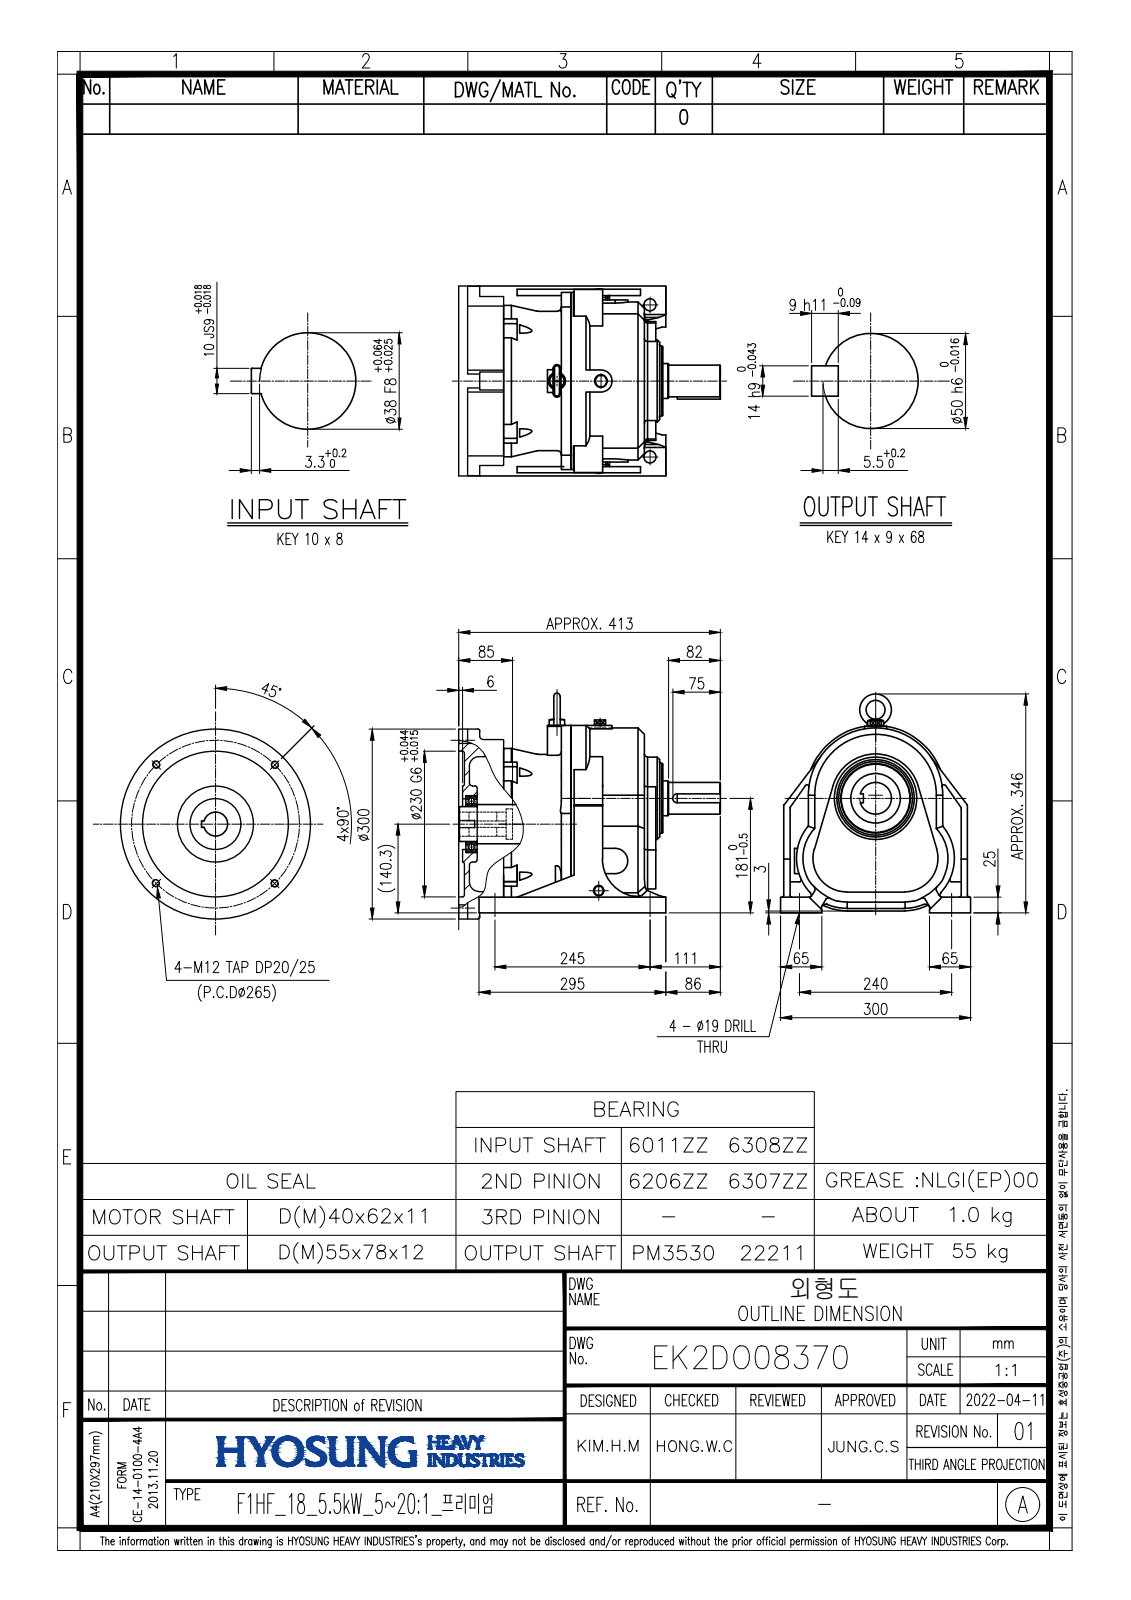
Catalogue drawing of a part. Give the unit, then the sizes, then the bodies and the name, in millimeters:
Units: millimetres
Overall size (bounding box): 413 × 356.75 × 309
Round holes (diameter × count): ⌀10.2 ×5, ⌀10 ×4, ⌀19 ×4, ⌀2.7 ×2, ⌀6.8 ×2, ⌀13 ×2, ⌀14 ×2, ⌀4 ×1, ⌀8.5 ×1, ⌀38 ×1, ⌀48 ×1, ⌀59.6 ×1
Round bosses / shafts (diameter × count): ⌀55 ×2, ⌀300 ×1, ⌀220 ×1, ⌀130 ×1, ⌀110 ×1, ⌀66.41 ×1, ⌀50 ×1, ⌀12 ×1
Partial cylindrical surfaces — rounded edges, fillets, slot ends (radius × count): R5 ×59, R7 ×17, R6 ×10, R11 ×6, R1 ×4, R12.5 ×4, R83 ×4, R3 ×3
Main face-to-face distances: 5, 9, 18, 153, 311, 295, 162, 302, 149, 25
Hole centre spacings: 181.81, 132.5, 8, 98.62, 101.41, 124.49, 176.06, 187.38
Volume: 16 850 000 mm³ · Surface area: 625 124 mm²
Bodies: 4 solids, 586 faces (263 planar, 197 cylindrical, 126 other)
Part name (STEP PRODUCT): EK2DO08370H001_F1HM18_5.5KW_R5~20_defeature
STEP written by: SolidWorks 2021 (AUTOMOTIVE_DESIGN)
